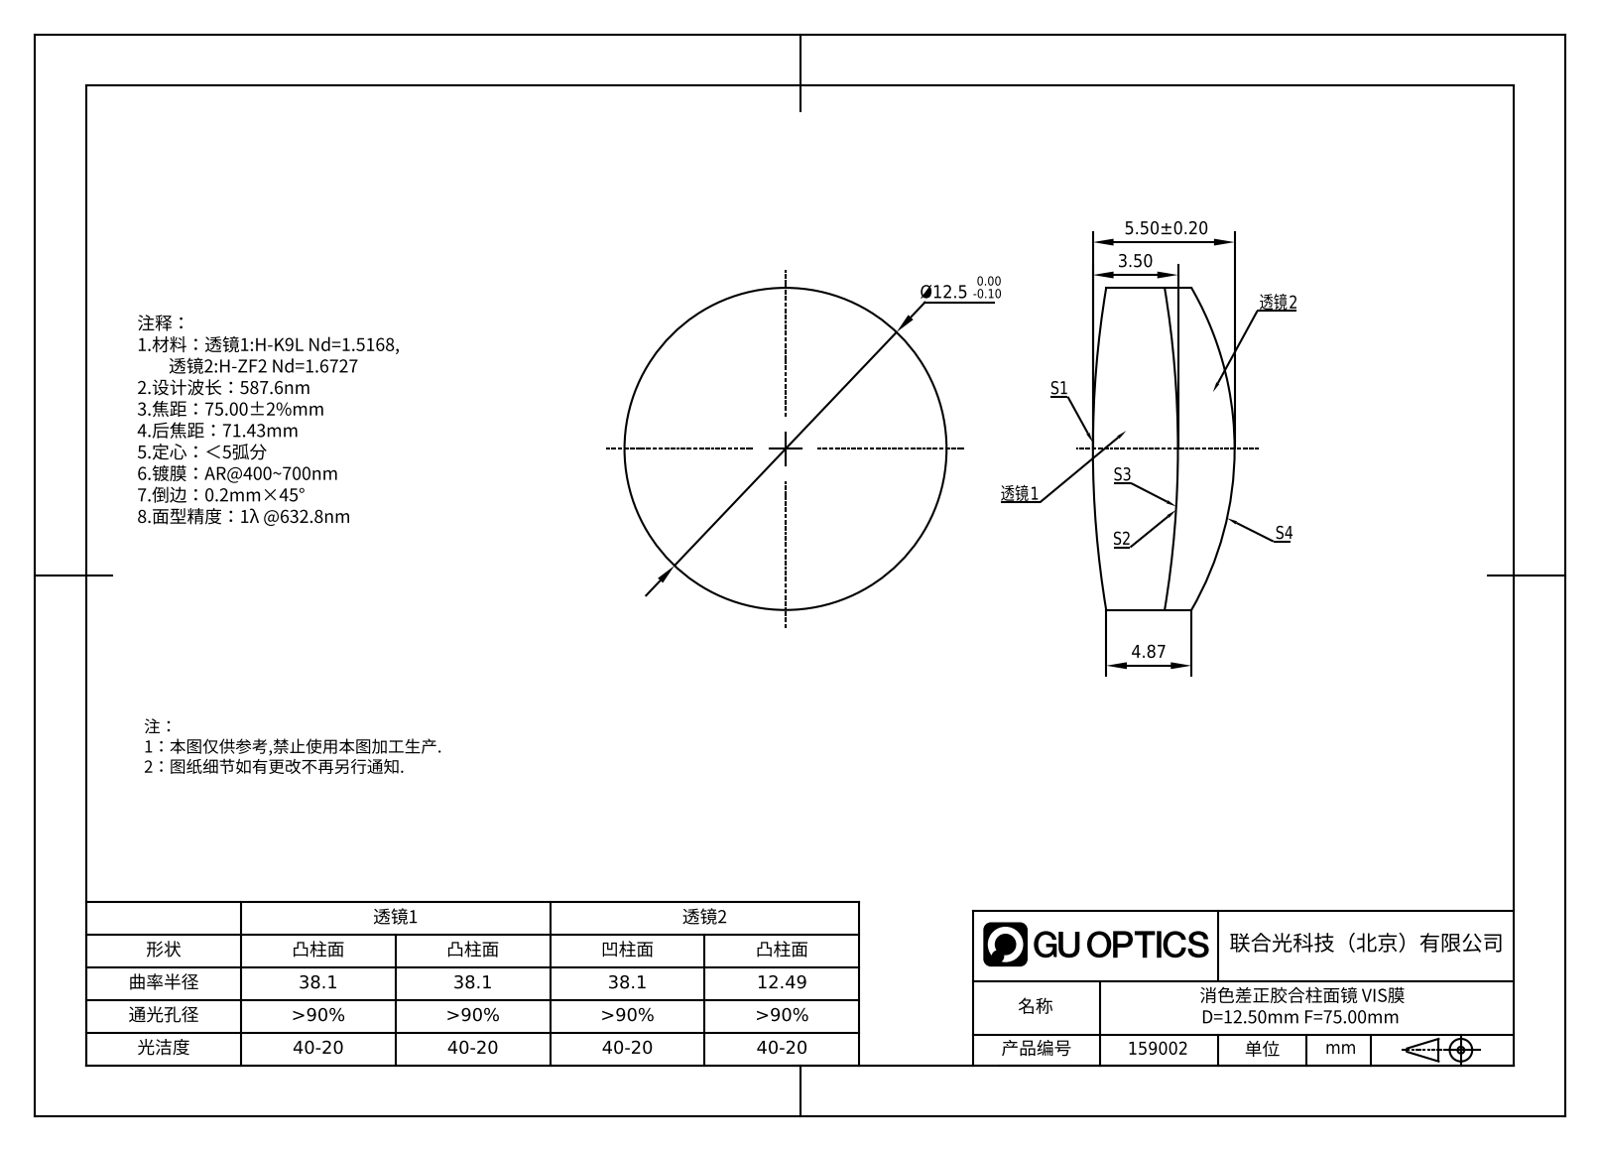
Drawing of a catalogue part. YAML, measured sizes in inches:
part_name: "159002"
step_written_by: "SolidWorks 2020 (CONFIG_CONTROL_DESIGN)"
units: inches
bodies: {solids: 1, faces: 5, planar: 0, cylindrical: 5, other: 0}
overall_size: [0.492, 0.492, 0.217]
volume: 0.037
surface_area: 0.657
round_bosses_or_shafts:
  - {diameter: 0.492, count: 1}
partial_cylinders:
  - {radius: 0.492, count: 1}
  - {radius: 1.5, count: 1}
